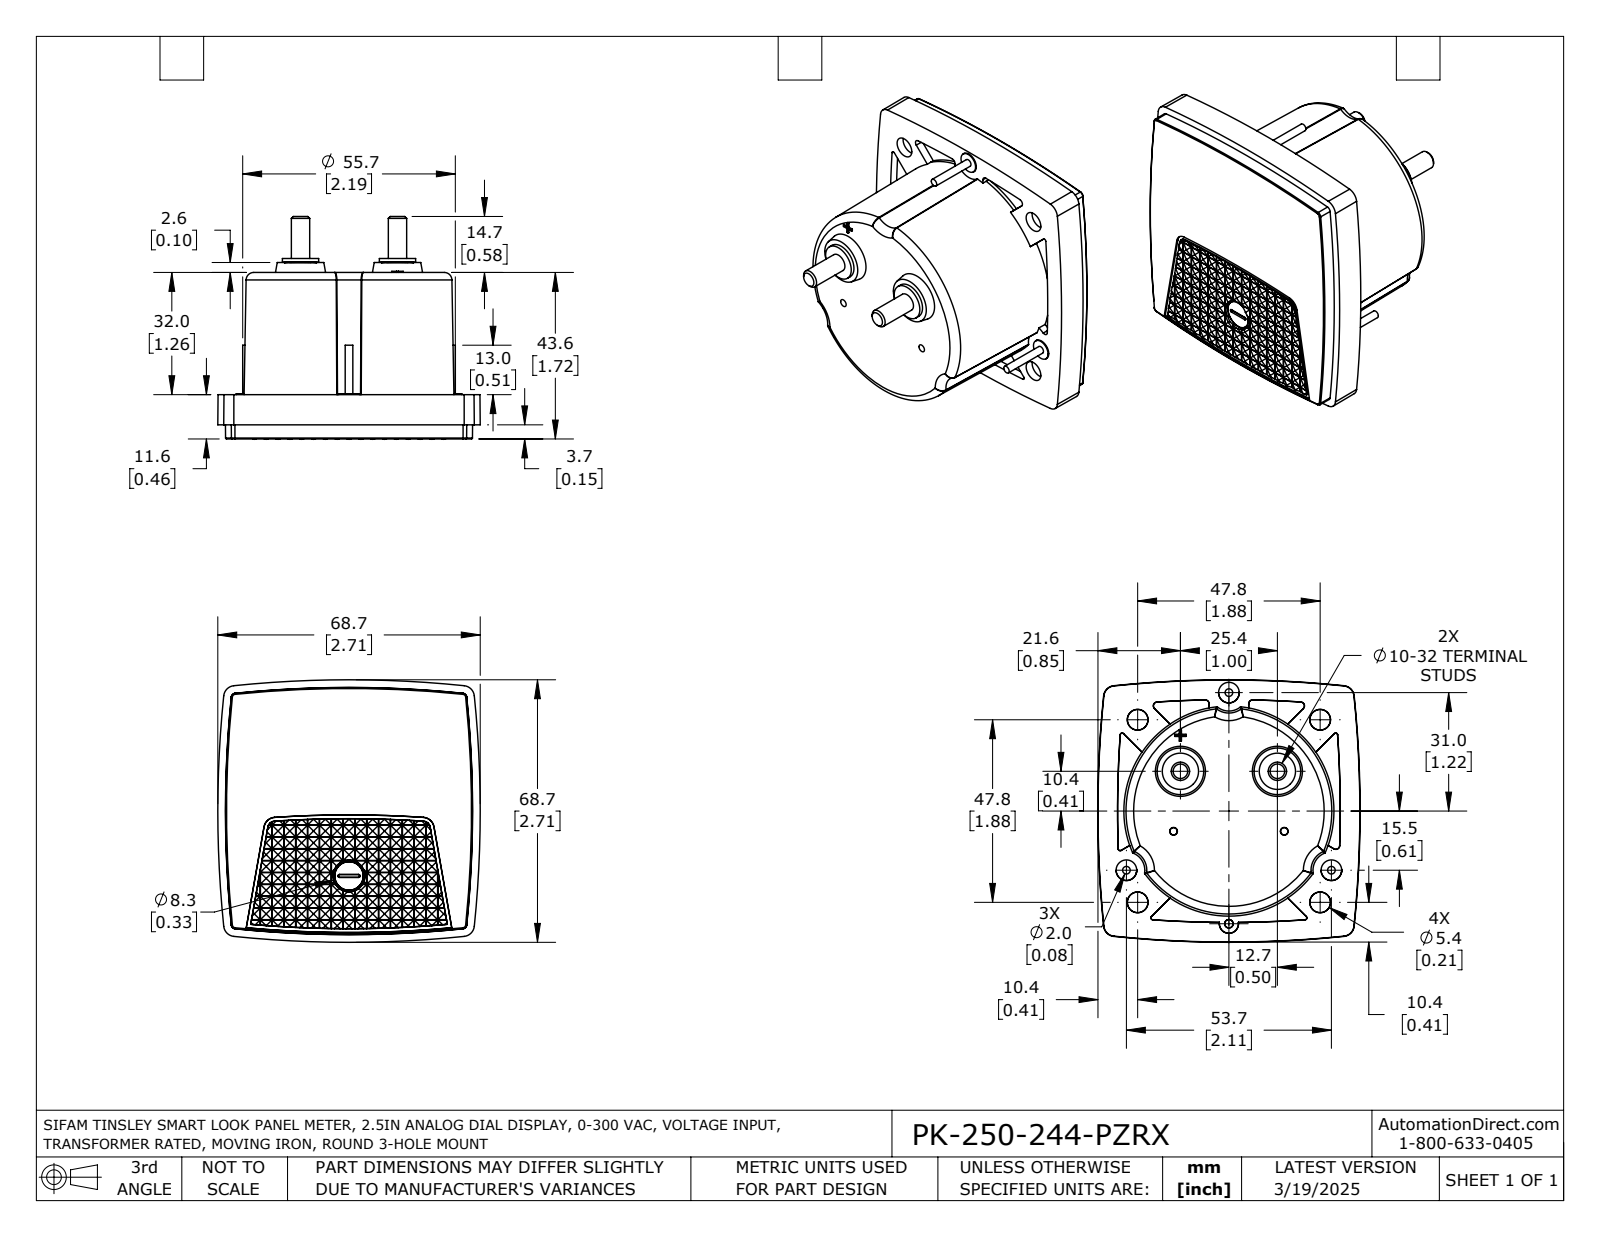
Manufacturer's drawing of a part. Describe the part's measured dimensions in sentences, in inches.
The part is named "PK-250-244-PZRX". Its 3-D file was written by "SolidWorks 2021 (AUTOMOTIVE_DESIGN)". It is 1 solid with 1550 faces: 1165 planar, 265 cylindrical and 120 other. Overall it measures 2.706 by 2.706 by 2.297 inches. Its volume is 7.594 cubic inches and its surface area 30.41 square inches. Round bosses or shafts: 3 of diameter 0.213, 3 of diameter 0.079, 2 of diameter 0.374, 2 of diameter 0.189, 1 of diameter 0.215. Partial cylindrical surfaces (rounded edges, fillets, slot ends): 2 of radius 0.167, 1 of radius 1.083. The main face-to-face distances are 1.717, 1.26, 0.457, 0.024, 0.087, 0.096, 0.311, 0.12, 0.072, 1.346.
